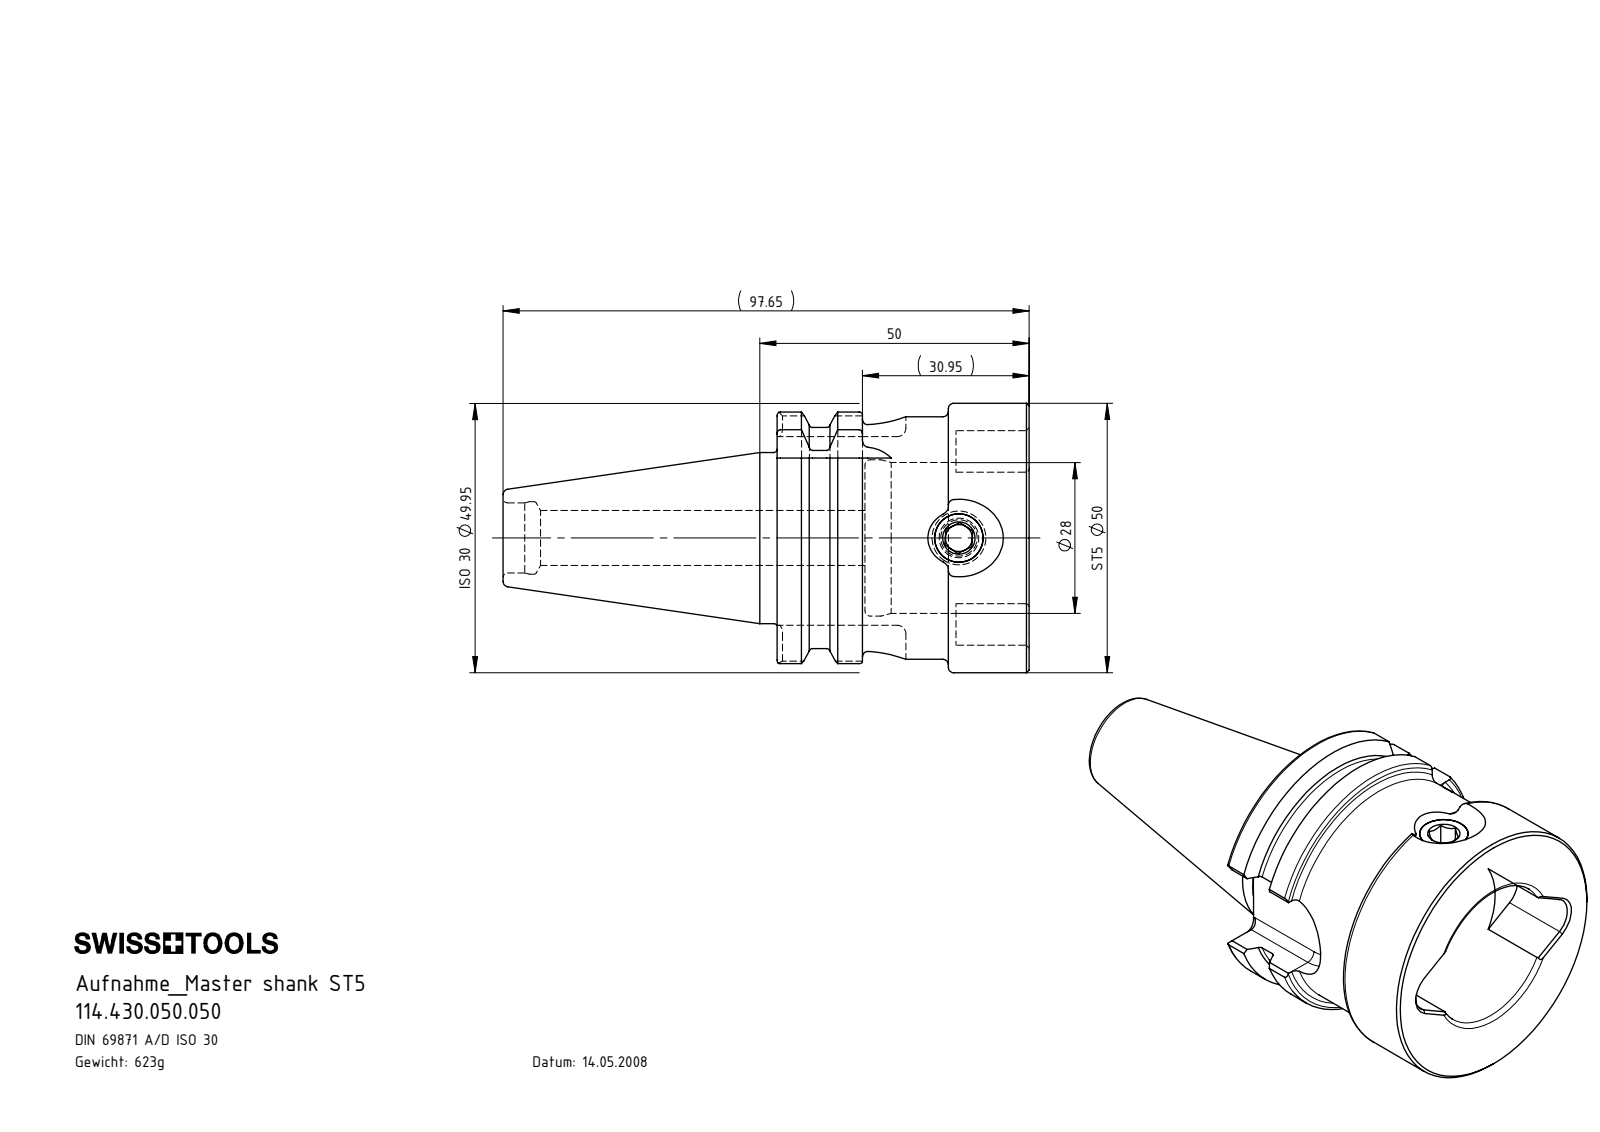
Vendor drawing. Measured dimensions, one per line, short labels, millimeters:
name: SK3-ST5.K01.050_B; ST5-ER1.001.012_A; SK3.ST5.K01.050
written by: SolidWorks 2017 (AUTOMOTIVE_DESIGN)
unit: mm
bodies: 2 solids, 130 faces (50 planar, 33 cylindrical, 47 other)
size: 97.65 × 50 × 50
volume: 79 426 mm³; area: 21 012 mm²
holes: 1× ⌀5, 1× ⌀9, 1× ⌀10.2, 1× ⌀13, 1× ⌀13.45, 1× ⌀28, 1× ⌀29
bosses: 1× ⌀50, 1× ⌀45, 1× ⌀31.75, 1× ⌀10
rounds: 8× R1.6, 2× R4.2, 1× R8, 1× R8.05, 1× R22.02, 1× R24.98
face distances: 46.8, 16.3, 30.5, 35, 24.1, 33.2, 16.9, 13.6, 15.85, 0.45
